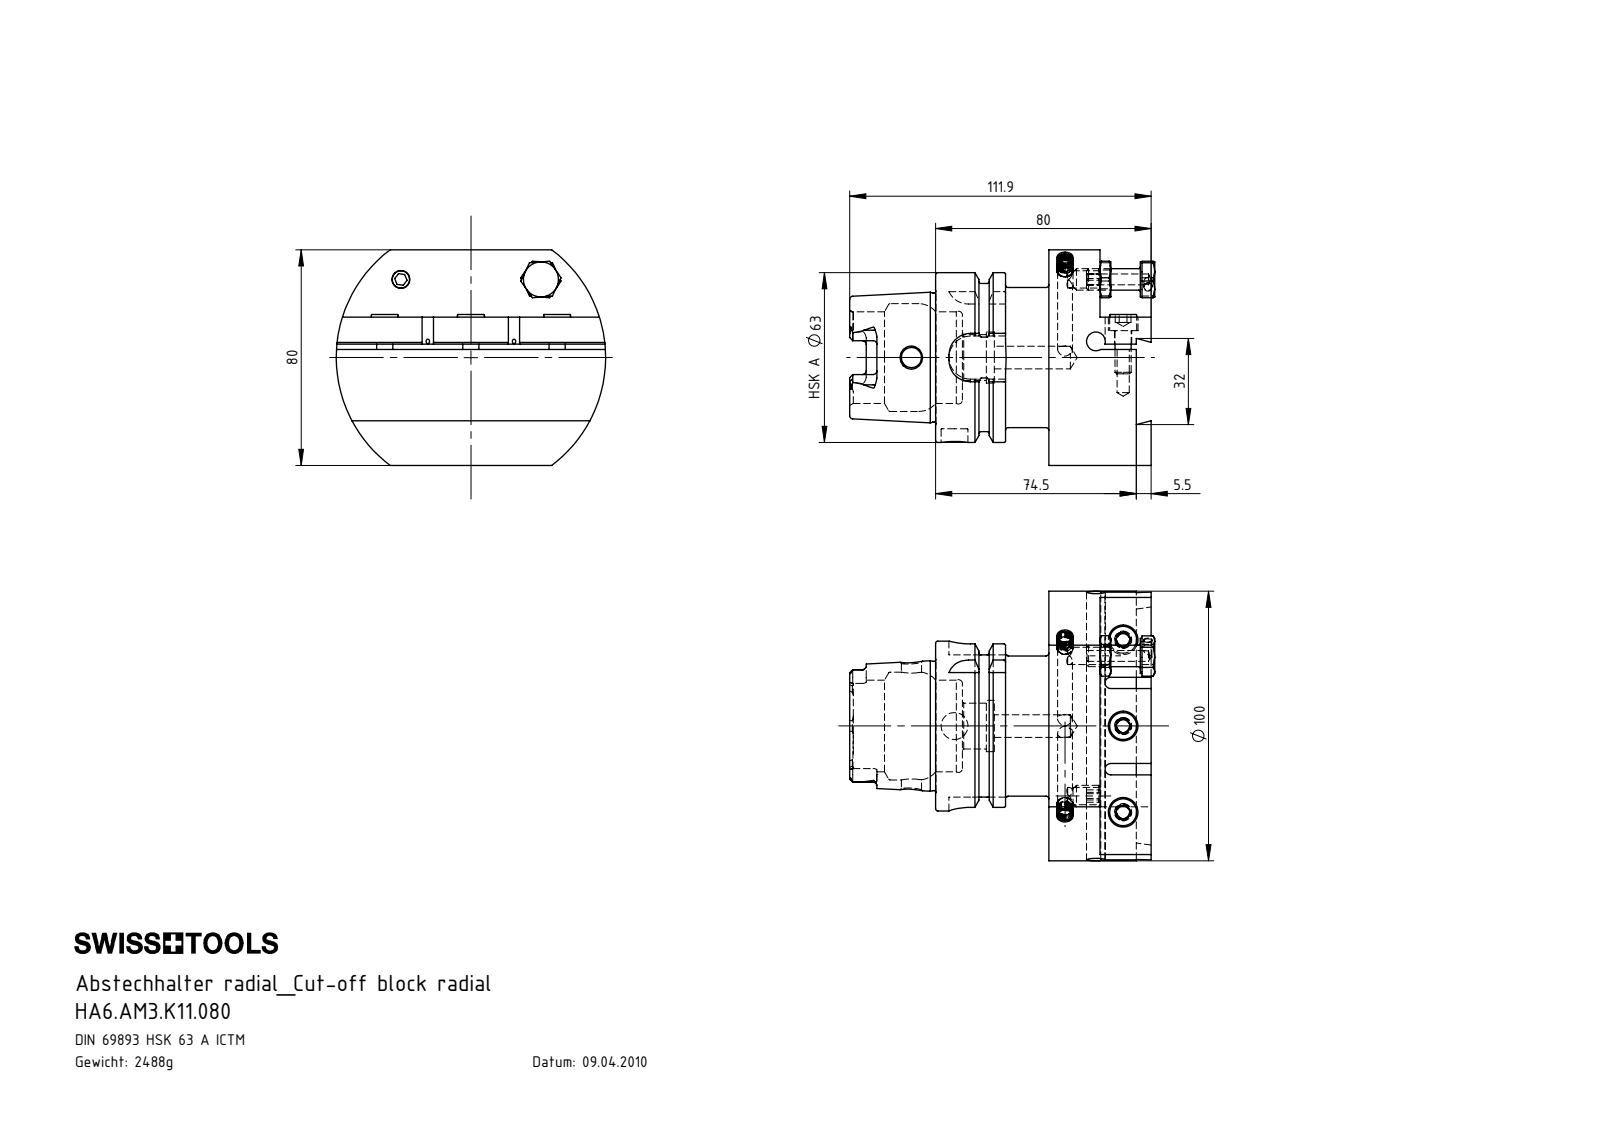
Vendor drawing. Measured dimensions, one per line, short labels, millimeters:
name: ISO 4035 - M8_PreviewCfg; ISO 4762 - M6 x 16_PreviewCfg; HA6.AM3.K11.080; HA6-AM3.K11.080_B_Fertigbearbeitung (+3 more)
written by: SolidWorks 2017 (AUTOMOTIVE_DESIGN)
unit: mm
bodies: 11 solids, 477 faces (153 planar, 120 cylindrical, 204 other)
size: 113.2 × 100 × 80
volume: 317 750 mm³; area: 59 610 mm²
holes: 5× ⌀6.4, 3× ⌀4.5, 3× ⌀11, 2× ⌀5, 2× ⌀5.5, 2× ⌀7, 1× ⌀3, 1× ⌀4, 1× ⌀7.5, 1× ⌀8.4, 1× ⌀10, 1× ⌀17
bosses: 5× ⌀6, 3× ⌀10, 2× ⌀8, 1× ⌀63, 1× ⌀54.95, 1× ⌀52, 1× ⌀47.94, 1× ⌀13
rounds: 4× R1.4, 4× R8, 2× R2.1, 2× R2.88, 1× R50
face distances: 19, 32.5, 38, 5.5, 80, 13.5, 55, 12, 43, 25
hole spacings: 32, 38.95, 70.22, 52, 62.5, 64, 68.76
